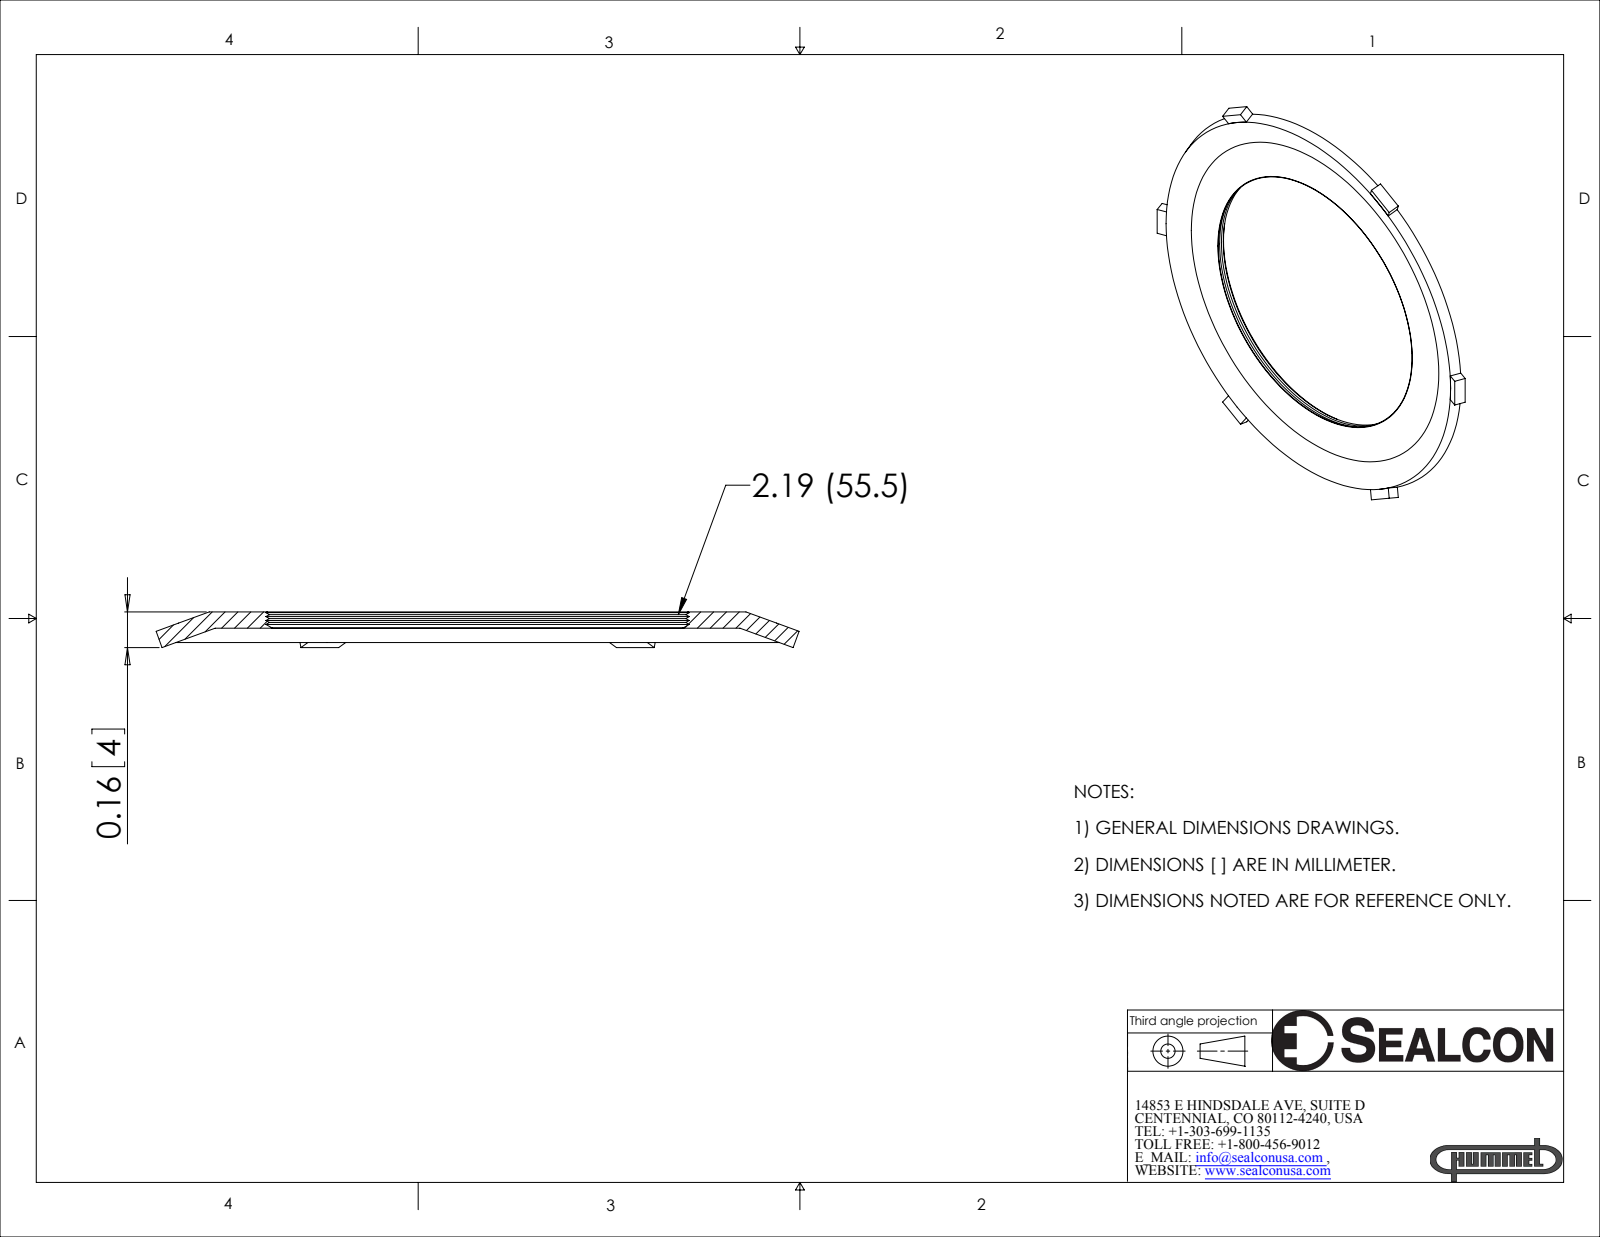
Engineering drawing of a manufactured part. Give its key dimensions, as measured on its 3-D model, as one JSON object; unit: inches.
{"part_name": "NN-36-ST", "step_written_by": "SolidWorks 2008 (CONFIG_CONTROL_DESIGN)", "units": "inches", "bodies": {"solids": 1, "faces": 72, "planar": 44, "cylindrical": 0, "other": 28}, "overall_size": [2.947, 2.82, 0.163], "volume_in3": 0.261, "surface_area_in2": 8.55, "face_to_face_distances": [0.074, 0.08, 0.2, 0.079, 0.11]}
